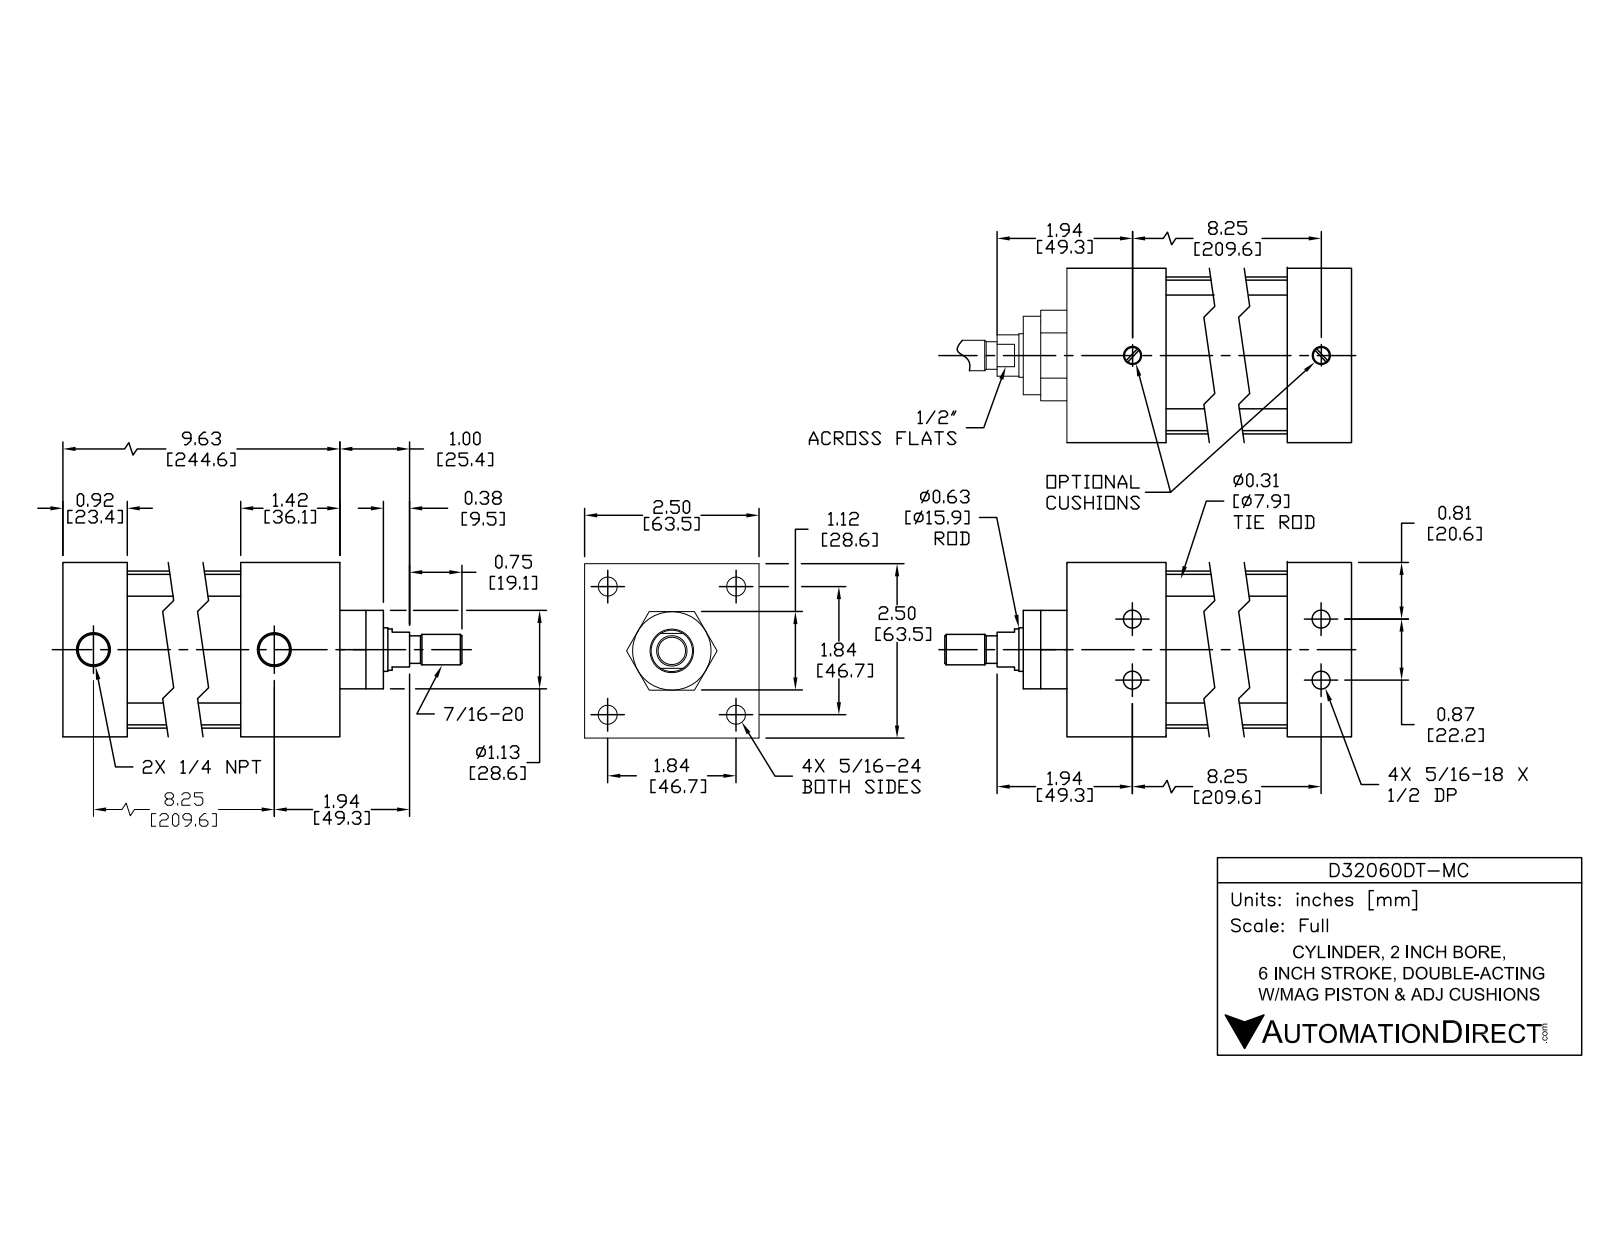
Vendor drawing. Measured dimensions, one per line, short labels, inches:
name: D32060DT-M BODY; D32060DT-M PISTON; D32060DT-MC
written by: SolidWorks 2015 (AUTOMOTIVE_DESIGN)
unit: in
bodies: 12 solids, 298 faces (94 planar, 114 cylindrical, 90 other)
size: 11.371 × 2.5 × 2.5
volume: 28.16 in³; area: 236.6 in²
holes: 4× ⌀0.252, 4× ⌀0.267, 4× ⌀0.359, 4× ⌀0.5, 2× ⌀0.297, 2× ⌀0.477, 1× ⌀0.625, 1× ⌀0.628, 1× ⌀2
bosses: 4× ⌀0.484, 4× ⌀0.313, 4× ⌀0.282, 1× ⌀2.25, 1× ⌀1.997, 1× ⌀1.12, 1× ⌀0.622, 1× ⌀0.59
rounds: 4× R0.25
face distances: 2.5, 9.621, 1.42, 8.201, 7.281, 8.701, 0.92, 1, 8.601, 7.181
hole spacings: 8.245, 0.437, 0.438, 0.875, 1.306, 1.307, 1.848, 1.848
